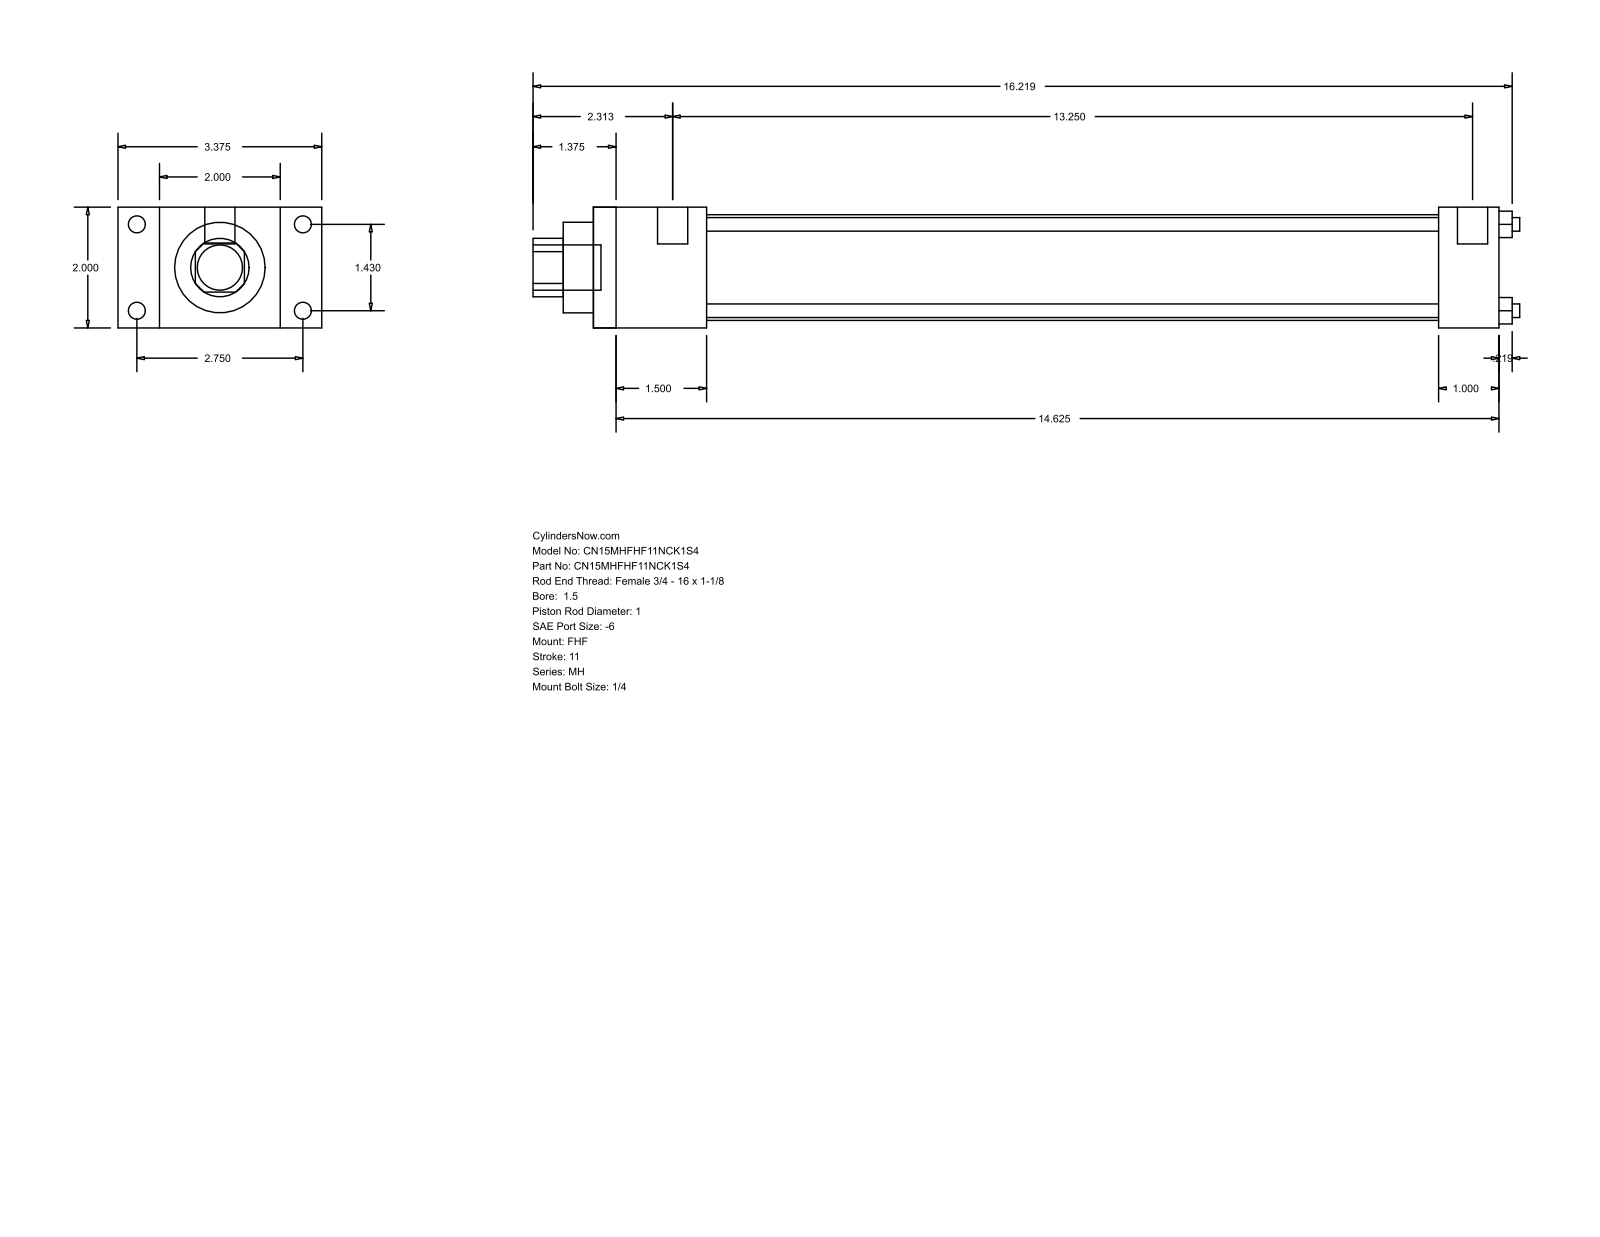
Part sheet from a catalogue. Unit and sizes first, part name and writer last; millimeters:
Units: millimetres
Overall size (bounding box): 415.13 × 85.72 × 50.8
Round holes (diameter × count): ⌀5.71 ×4, ⌀25.4 ×1, ⌀38.1 ×1, ⌀44.45 ×1
Round bosses / shafts (diameter × count): ⌀7.14 ×4, ⌀5.56 ×4, ⌀12.7 ×2, ⌀19.05 ×1
Partial cylindrical surfaces — rounded edges, fillets, slot ends (radius × count): R12.29 ×1
Main face-to-face distances: 50.8, 17.46, 68.26, 47.63, 85.72, 381, 333.37, 25.4, 355.6, 307.97
Hole centre spacings: 25.68, 36.32, 51.36
Bodies: 0 solids, 88 faces (60 planar, 28 cylindrical, 0 other)
Part name (STEP PRODUCT): MH_FHF__0150_1
STEP written by: GSSL Pune (CONFIG_CONTROL_DESIGN)
